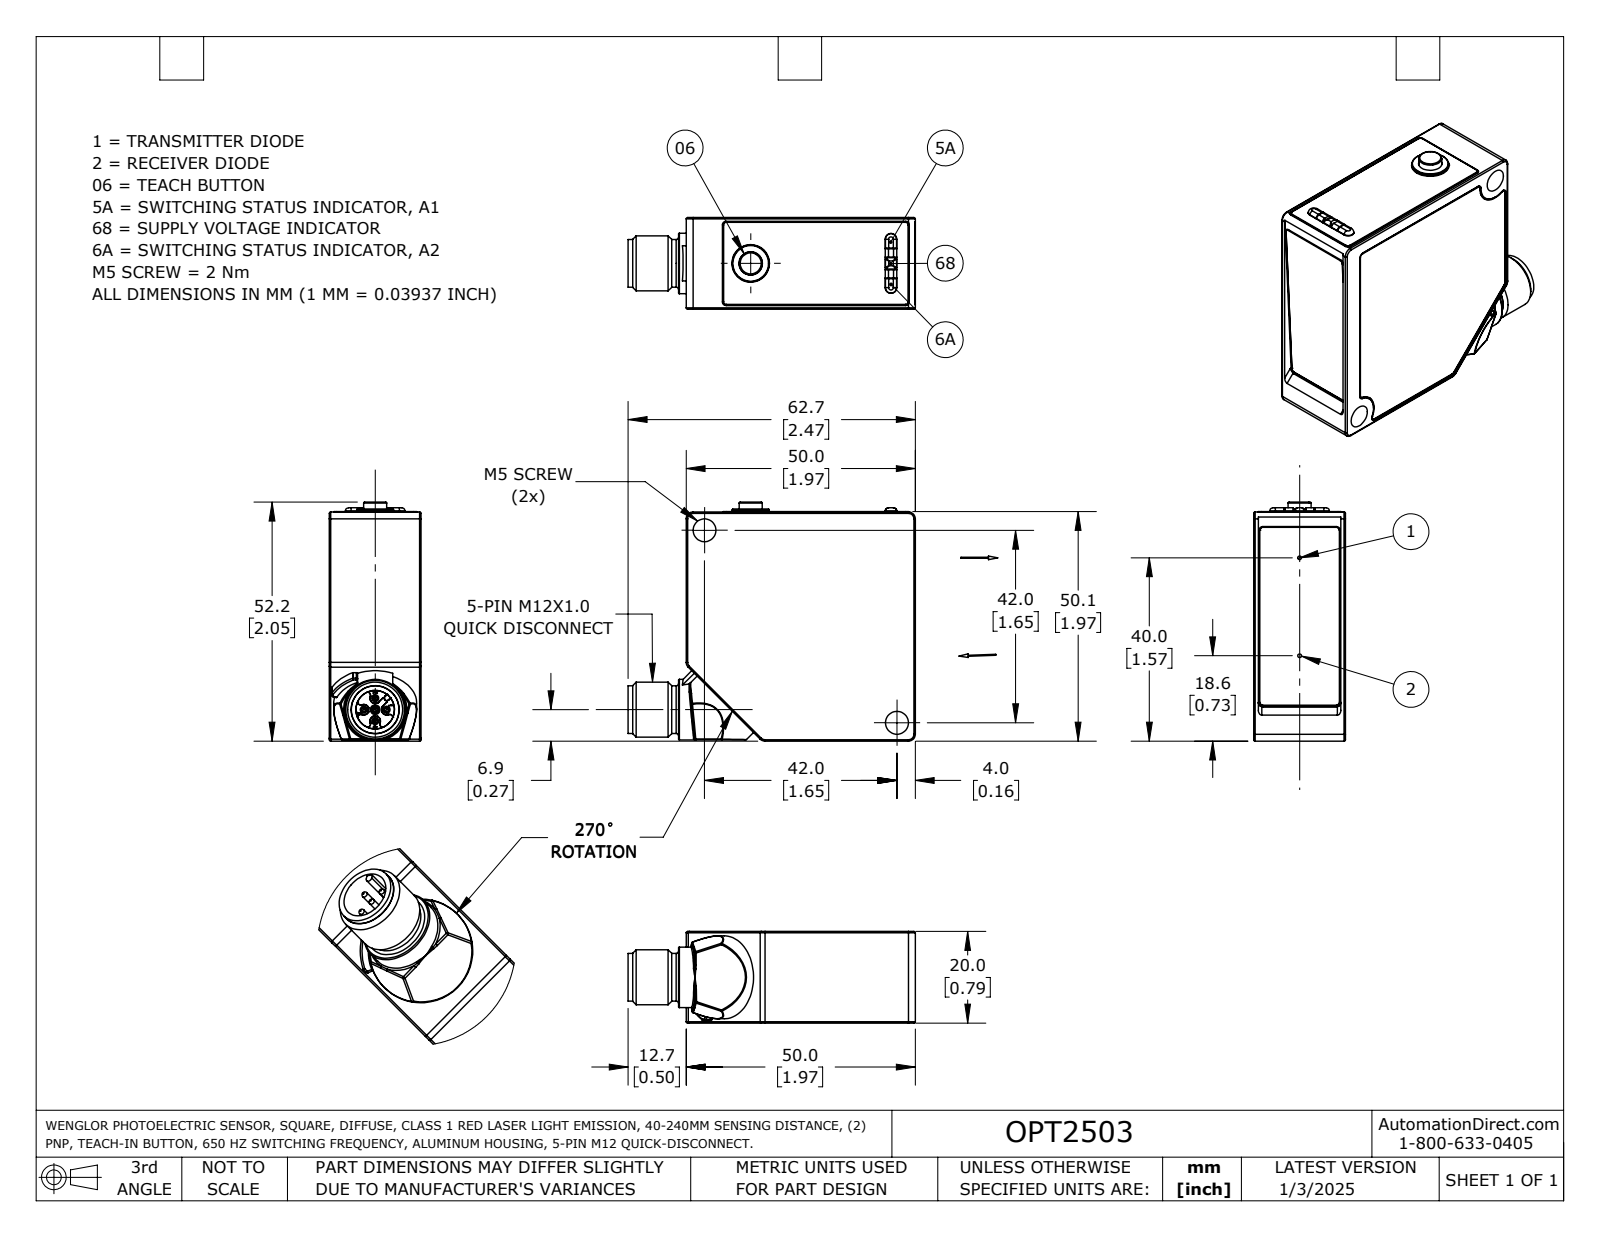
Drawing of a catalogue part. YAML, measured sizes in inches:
part_name: "OPT2500_OPT2503_OPT2506_OPT2509_OPT2512"
step_written_by: "SolidWorks 2024 (AUTOMOTIVE_DESIGN)"
units: inches
bodies: {solids: 3, faces: 407, planar: 171, cylindrical: 121, other: 115}
overall_size: [3.176, 2.053, 0.787]
volume: 3.014
surface_area: 15.72
round_holes:
  - {diameter: 0.06, count: 5}
  - {diameter: 0.201, count: 1}
round_bosses_or_shafts:
  - {diameter: 0.039, count: 5}
  - {diameter: 0.008, count: 2}
  - {diameter: 0.713, count: 1}
  - {diameter: 0.52, count: 1}
  - {diameter: 0.472, count: 1}
  - {diameter: 0.409, count: 1}
  - {diameter: 0.315, count: 1}
  - {diameter: 0.197, count: 1}
partial_cylinders:
  - {radius: 0.012, count: 30}
  - {radius: 0.026, count: 11}
  - {radius: 0.031, count: 7}
  - {radius: 0.028, count: 6}
  - {radius: 0.03, count: 6}
  - {radius: 0.059, count: 5}
  - {radius: 0.004, count: 4}
  - {radius: 0.027, count: 4}
face_to_face_distances: [0.785, 1.972, 0.787, 1.969, 1.958, 1.962, 0.039, 0.748, 0.031, 0.709]
hole_center_spacings: [0.098, 0.139, 0.197]
